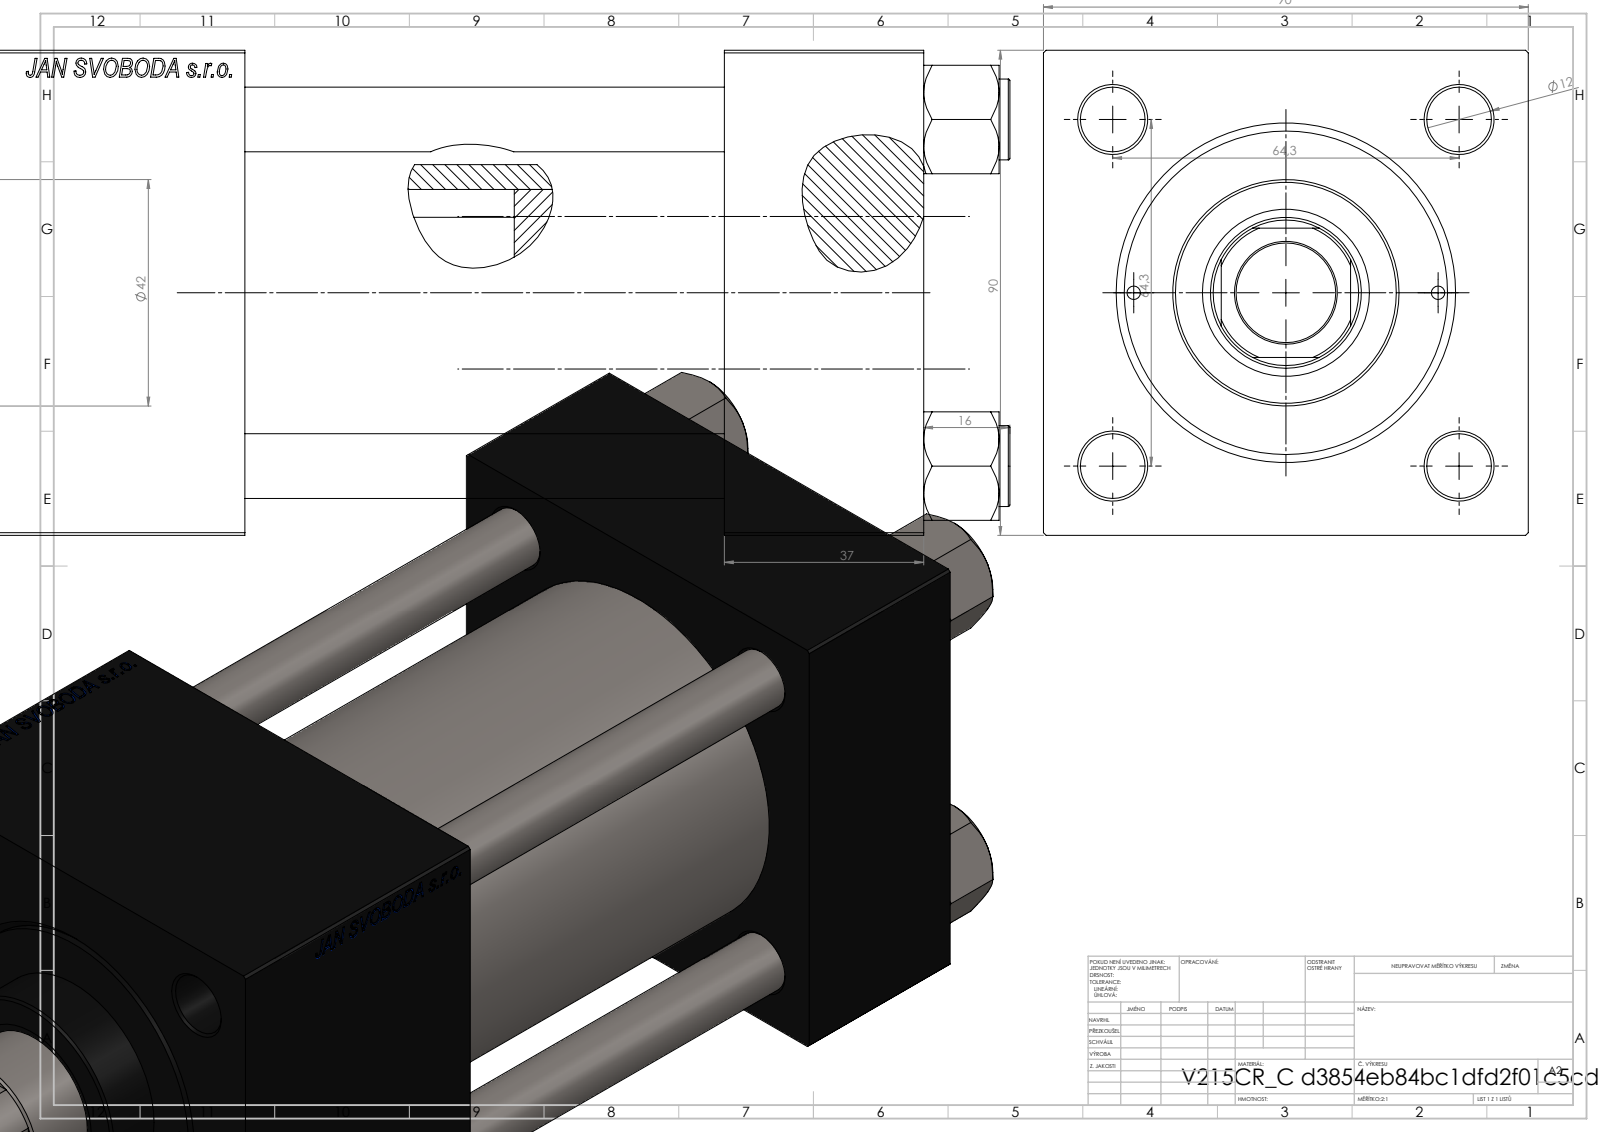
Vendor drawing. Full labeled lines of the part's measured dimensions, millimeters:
Part name (STEP PRODUCT): V215CR_VCP_C; V215CR_C_TYCINKA; NUT_M5_C; V215_VC_A (+1 more)
STEP written by: SolidWorks 2019 (CONFIG_CONTROL_DESIGN)
Units: millimetres
Bodies: 11 solids, 1154 faces (528 planar, 90 cylindrical, 536 other)
Overall size (bounding box): 233 × 90 × 90
Volume: 997 541 mm³ · Surface area: 198 811 mm²
Round holes (diameter × count): ⌀12 ×4, ⌀2.5 ×2, ⌀7 ×2, ⌀20.96 ×2, ⌀30 ×2, ⌀18.5 ×1, ⌀28 ×1, ⌀31 ×1, ⌀50 ×1, ⌀60 ×1, ⌀63 ×1
Round bosses / shafts (diameter × count): ⌀15 ×4, ⌀69 ×1, ⌀42 ×1
Partial cylindrical surfaces — rounded edges, fillets, slot ends (radius × count): R13.5 ×1
Main face-to-face distances: 90, 37, 185, 148, 126, 89, 59, 156.3, 119.3, 30.3
Hole centre spacings: 32.39, 45.47, 64.3, 68.42, 28.25, 90.93, 56.5, 127.5
